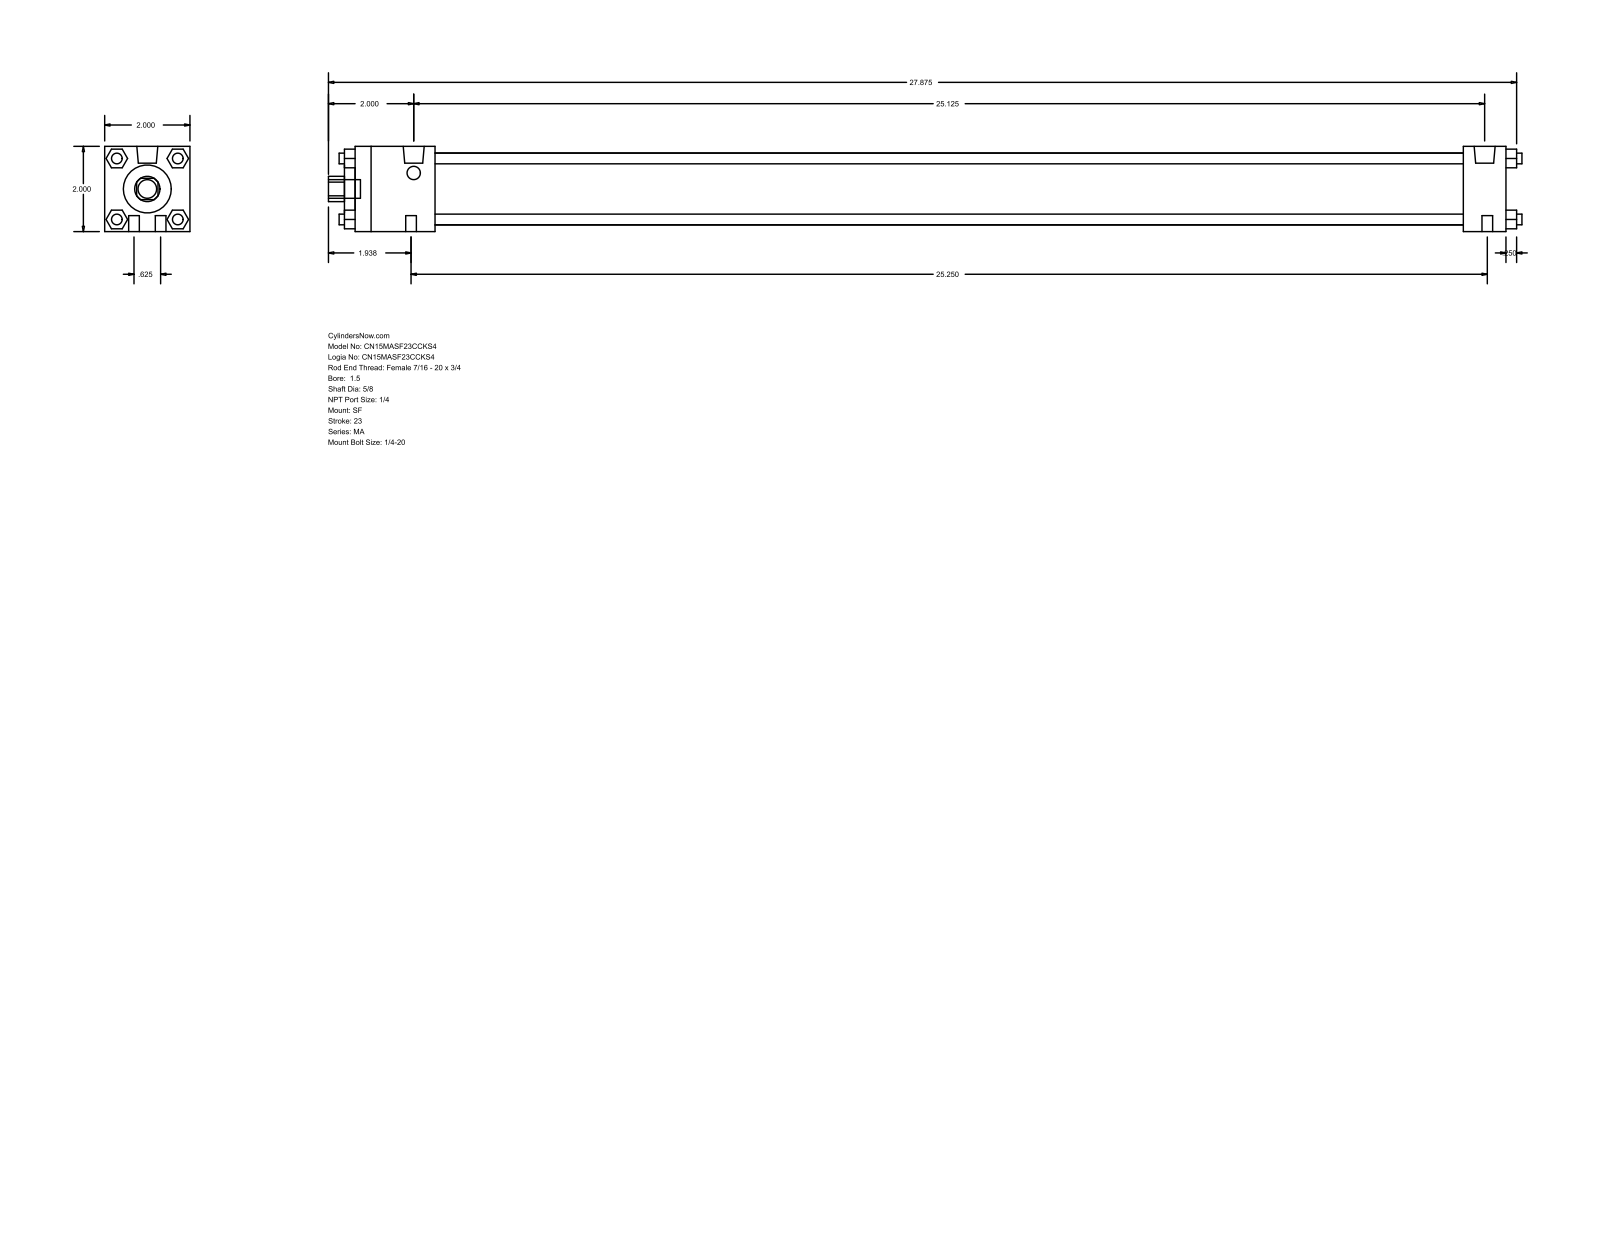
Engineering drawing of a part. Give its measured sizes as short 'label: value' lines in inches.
name: MA_SF__0150_0.625
written by: GSSL Pune (CONFIG_CONTROL_DESIGN)
unit: in
bodies: 0 solids, 124 faces (94 planar, 30 cylindrical, 0 other)
size: 28 × 2 × 2
holes: 1× ⌀0.625, 1× ⌀1.125, 1× ⌀1.69
bosses: 8× ⌀0.25, 2× ⌀0.492, 2× ⌀0.313, 1× ⌀0.437
rounds: 1× R0.297
face distances: 2, 27, 0.25, 27.25, 1.875, 26, 24.125, 25.125, 1, 2.125
